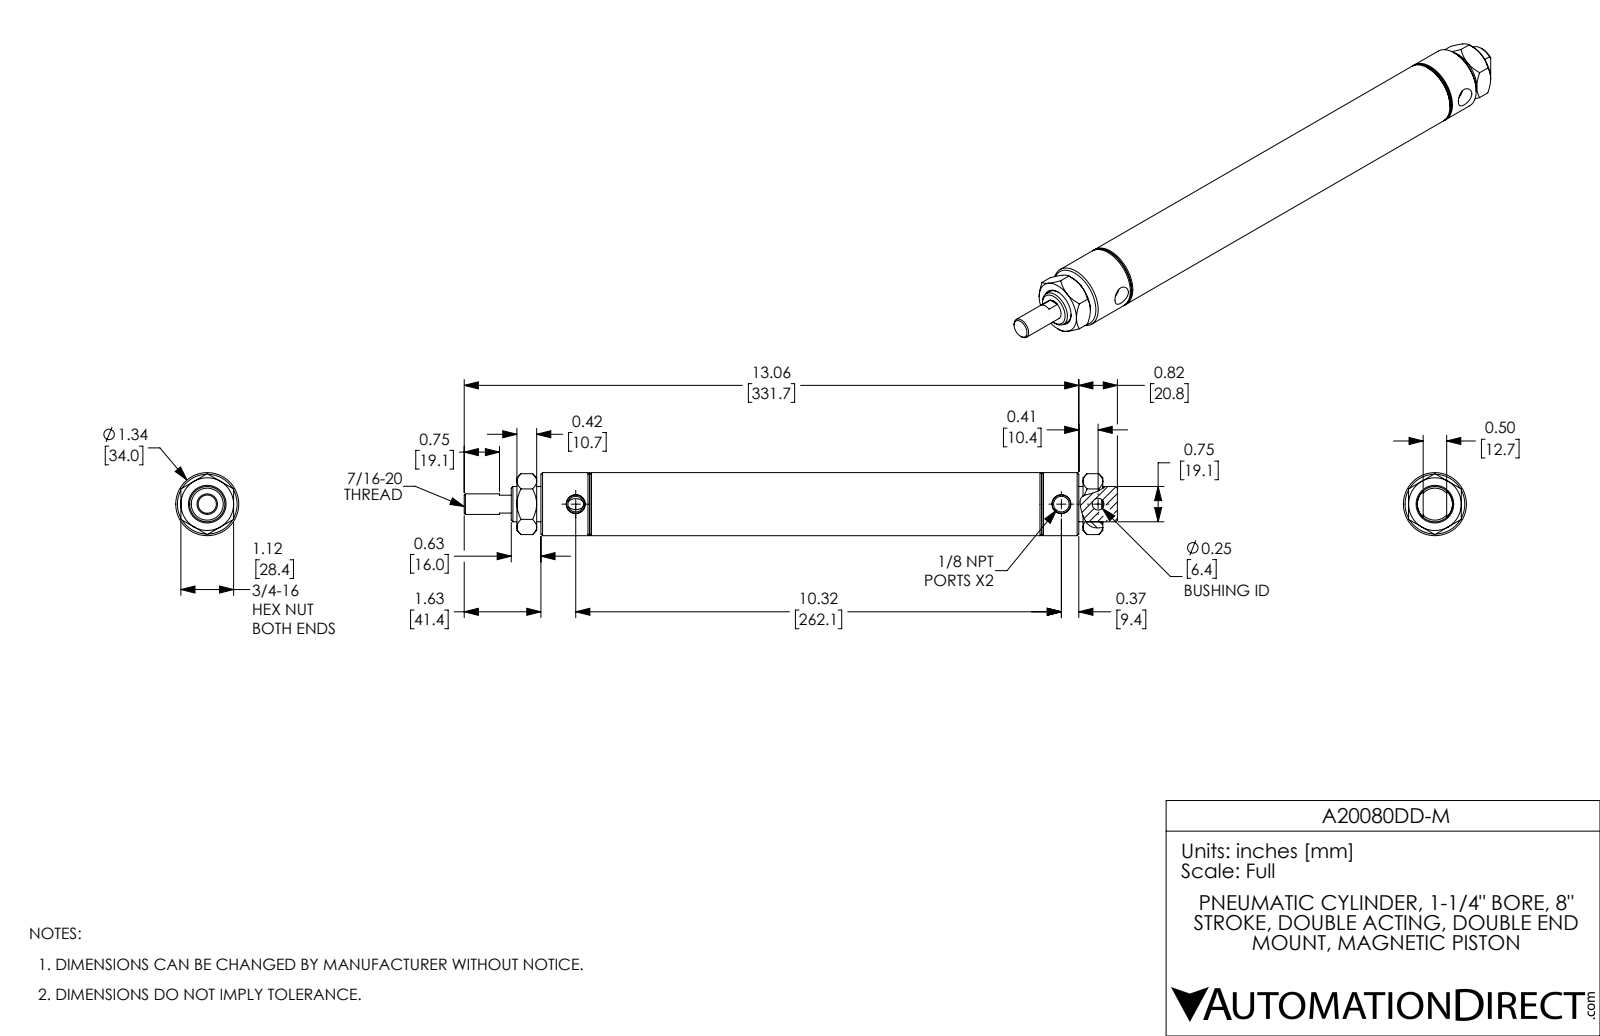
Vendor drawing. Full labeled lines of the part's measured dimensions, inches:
Part name (STEP PRODUCT): A20080DD-M_Mounting Nut_D-3556; A20080DD-M-Rod; A20080DD-M-MainBody; A20080DD-M
STEP written by: SolidWorks 2017 (AUTOMOTIVE_DESIGN)
Units: inches
Bodies: 4 solids, 138 faces (44 planar, 36 cylindrical, 58 other)
Overall size (bounding box): 13.88 × 1.34 × 1.34
Volume: 8.604 in³ · Surface area: 121.4 in²
Round holes (diameter × count): ⌀0.332 ×2, ⌀0.251 ×1, ⌀0.437 ×1, ⌀0.75 ×1, ⌀1.25 ×1
Round bosses / shafts (diameter × count): ⌀1.34 ×1, ⌀0.747 ×1
Main face-to-face distances: 1.465, 9.965, 0.5, 1.12, 8.5, 8, 0.31, 0.42, 12.03, 1.965
Hole centre spacings: 0.78, 10.32, 11.1
